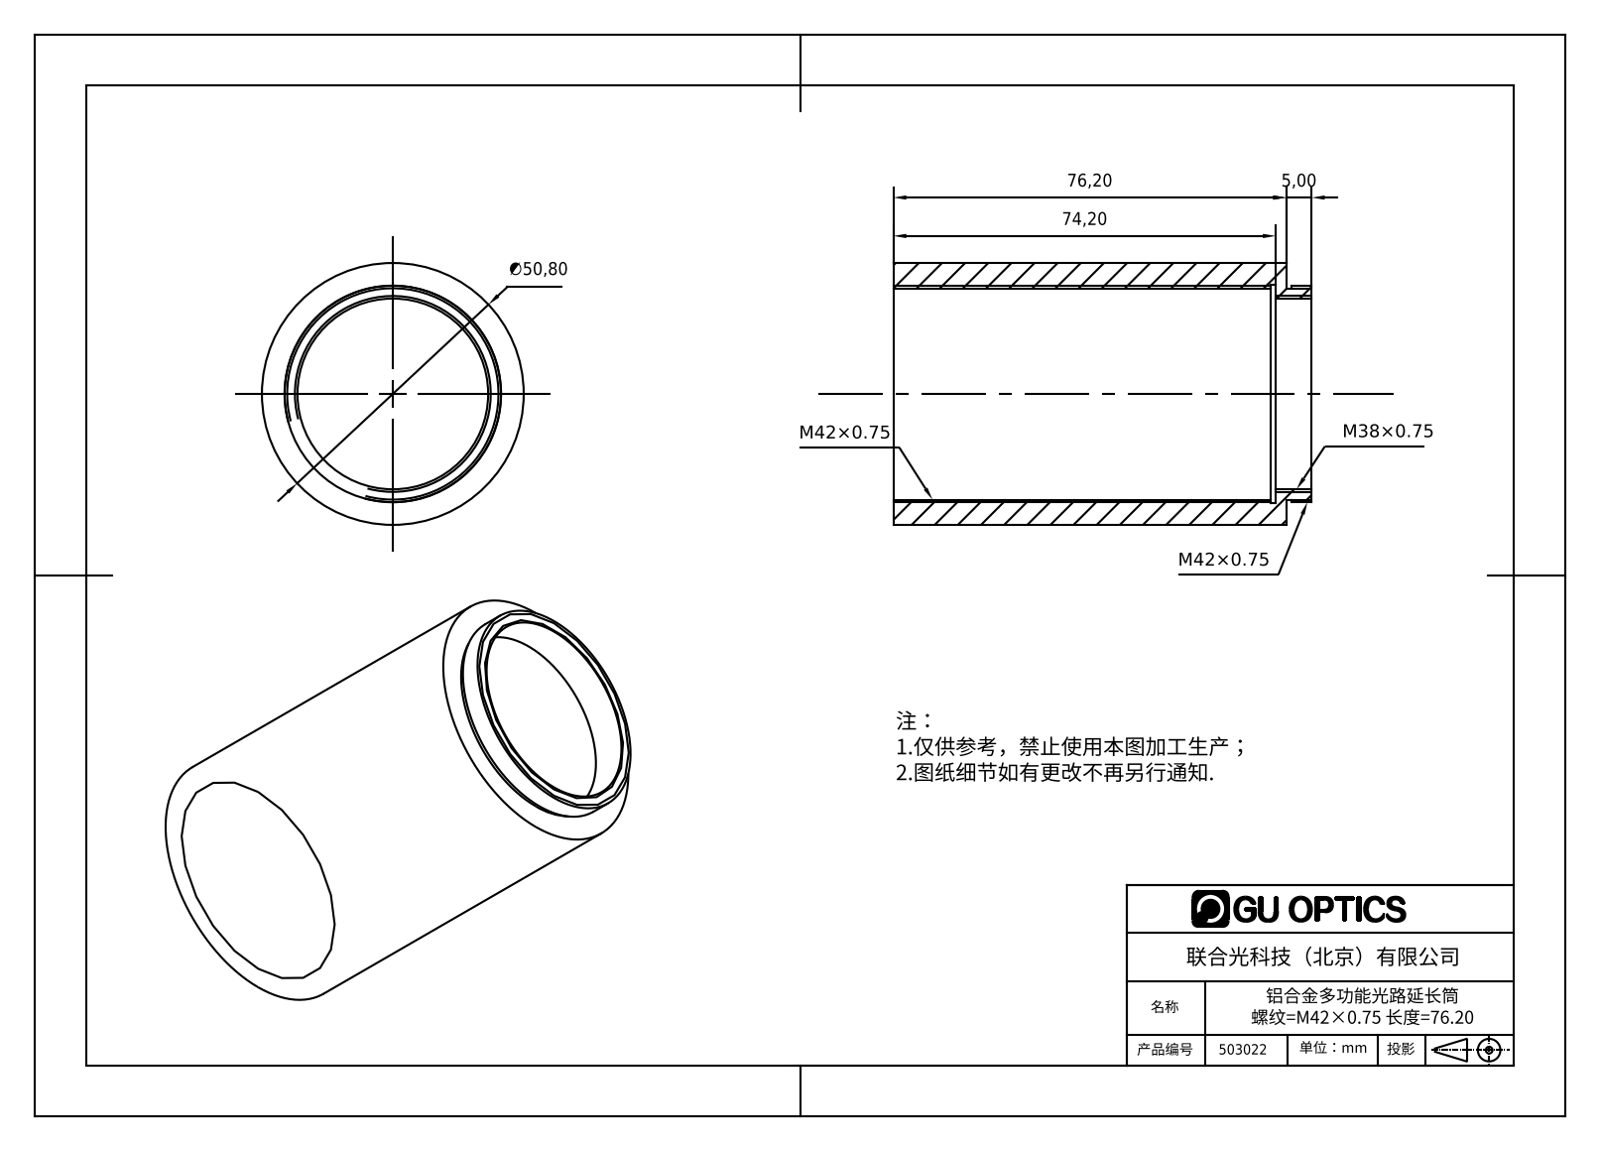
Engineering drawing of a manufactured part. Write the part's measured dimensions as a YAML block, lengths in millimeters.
part_name: "503022"
step_written_by: "SolidWorks 2016 (AUTOMOTIVE_DESIGN)"
units: millimeters
bodies: {solids: 1, faces: 18, planar: 6, cylindrical: 12, other: 0}
overall_size: [81.2, 50.8, 50.8]
volume: 55739
surface_area: 25383
round_holes:
  - {diameter: 37, count: 1}
  - {diameter: 41, count: 1}
  - {diameter: 42.2, count: 1}
round_bosses_or_shafts:
  - {diameter: 50.8, count: 1}
  - {diameter: 42, count: 1}
face_to_face_distances: [76.2, 74.2, 2, 81.2, 7, 5, 1, 3, 4, 73.2]
